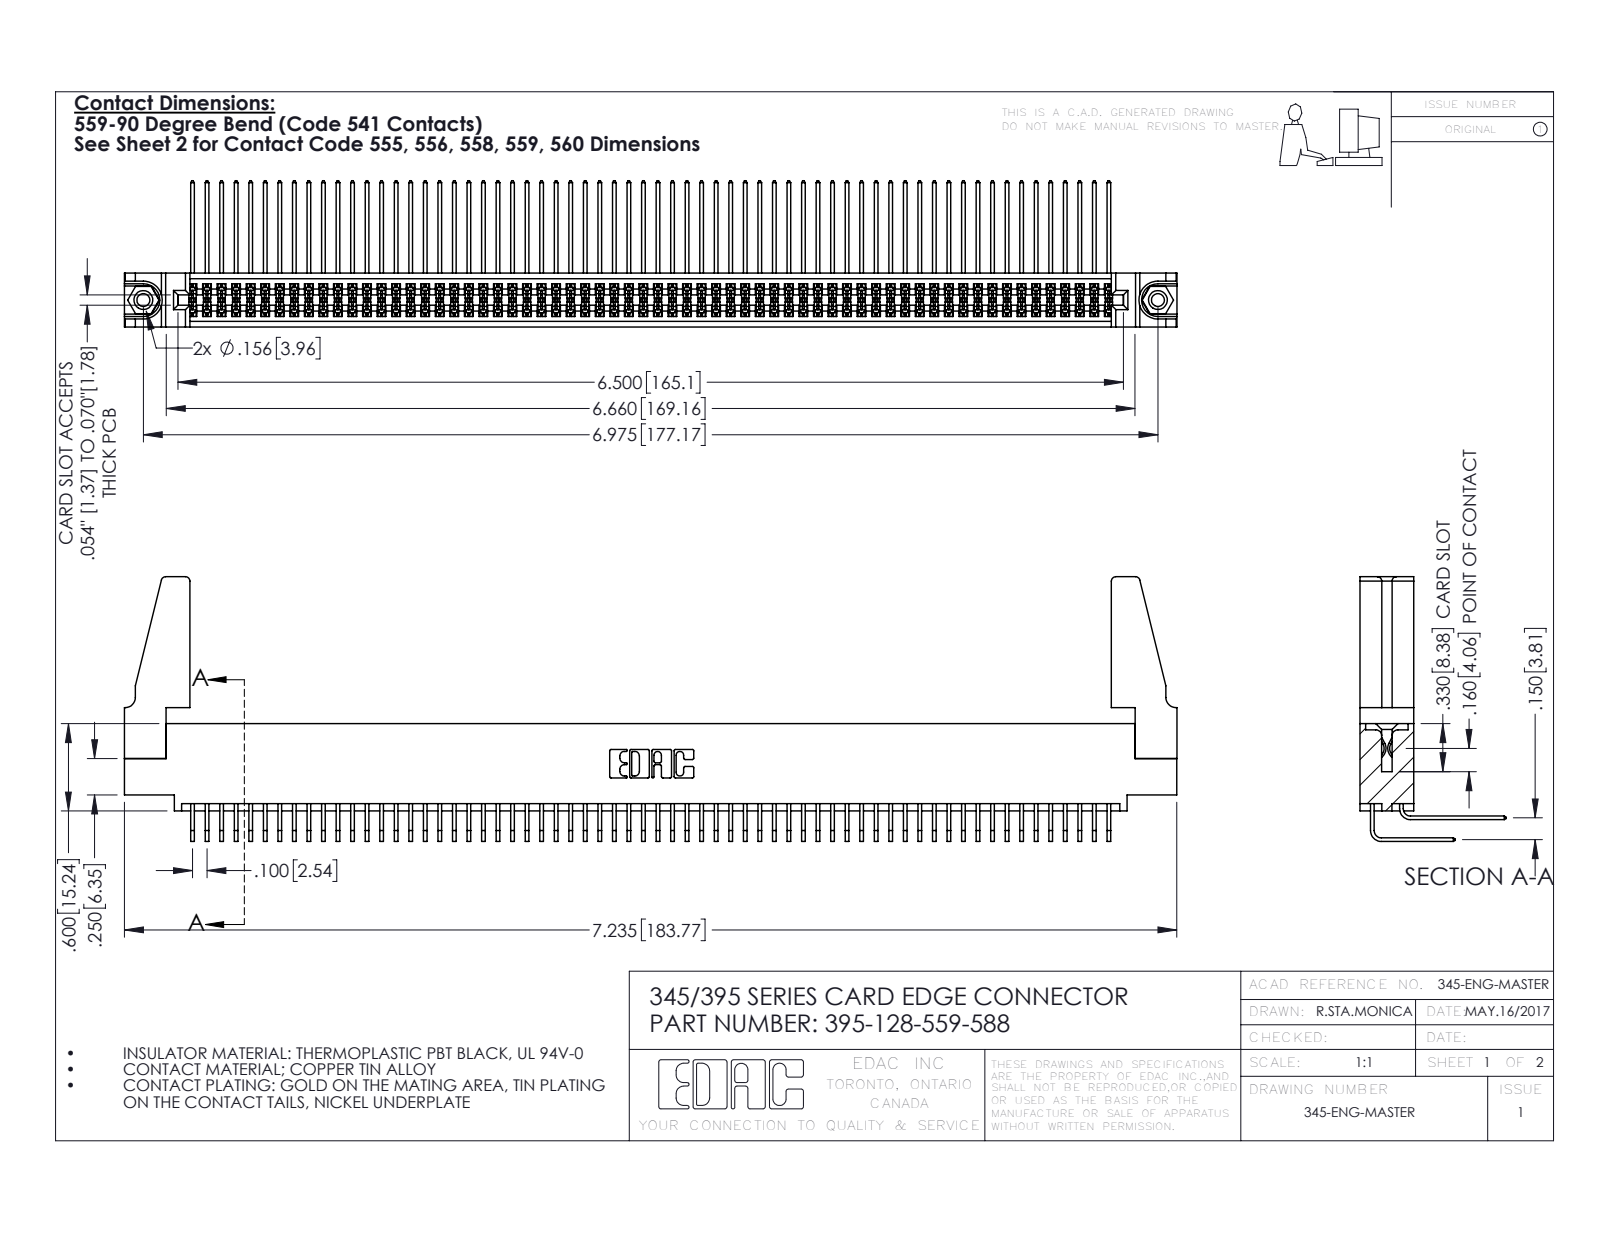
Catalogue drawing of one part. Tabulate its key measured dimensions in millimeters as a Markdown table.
| quantity | value |
| --- | --- |
| part name | 345-220-078_345-220-088; 395-128-559-588; 345 Part_0.110 Offset - 0.156 Dia-TH; 345-292-001_558 559 Tail - 1 (+2 more) |
| STEP written by | SolidWorks 2016 (CONFIG_CONTROL_DESIGN) |
| units | millimeters |
| bodies | 133 solids, 6910 faces (4636 planar, 2258 cylindrical, 16 other) |
| overall size | 183.8 × 46.2 × 25.5 |
| volume | 21 980 mm³ |
| surface area | 34 790 mm² |
| round holes (diameter × count) | 2.3 × 2, 3.2 × 2, 4 × 2, 1.6 × 1 |
| round bosses / shafts (diameter × count) | 3.9 × 2 |
| partial cylindrical surfaces (radius × count) | 0.2 × 193, 0.3 × 22, 0.8 × 8, 0.2 × 6, 0.8 × 6, 0.7 × 3, 0.4 × 2, 0.5 × 2 |
| main face-to-face distances | 1.8, 7.6, 9.4, 2.5, 6.9, 0.6, 5.1, 5.7, 4.4, 3.8 |
| hole center spacings | 6.9, 171.2, 177.2 |
